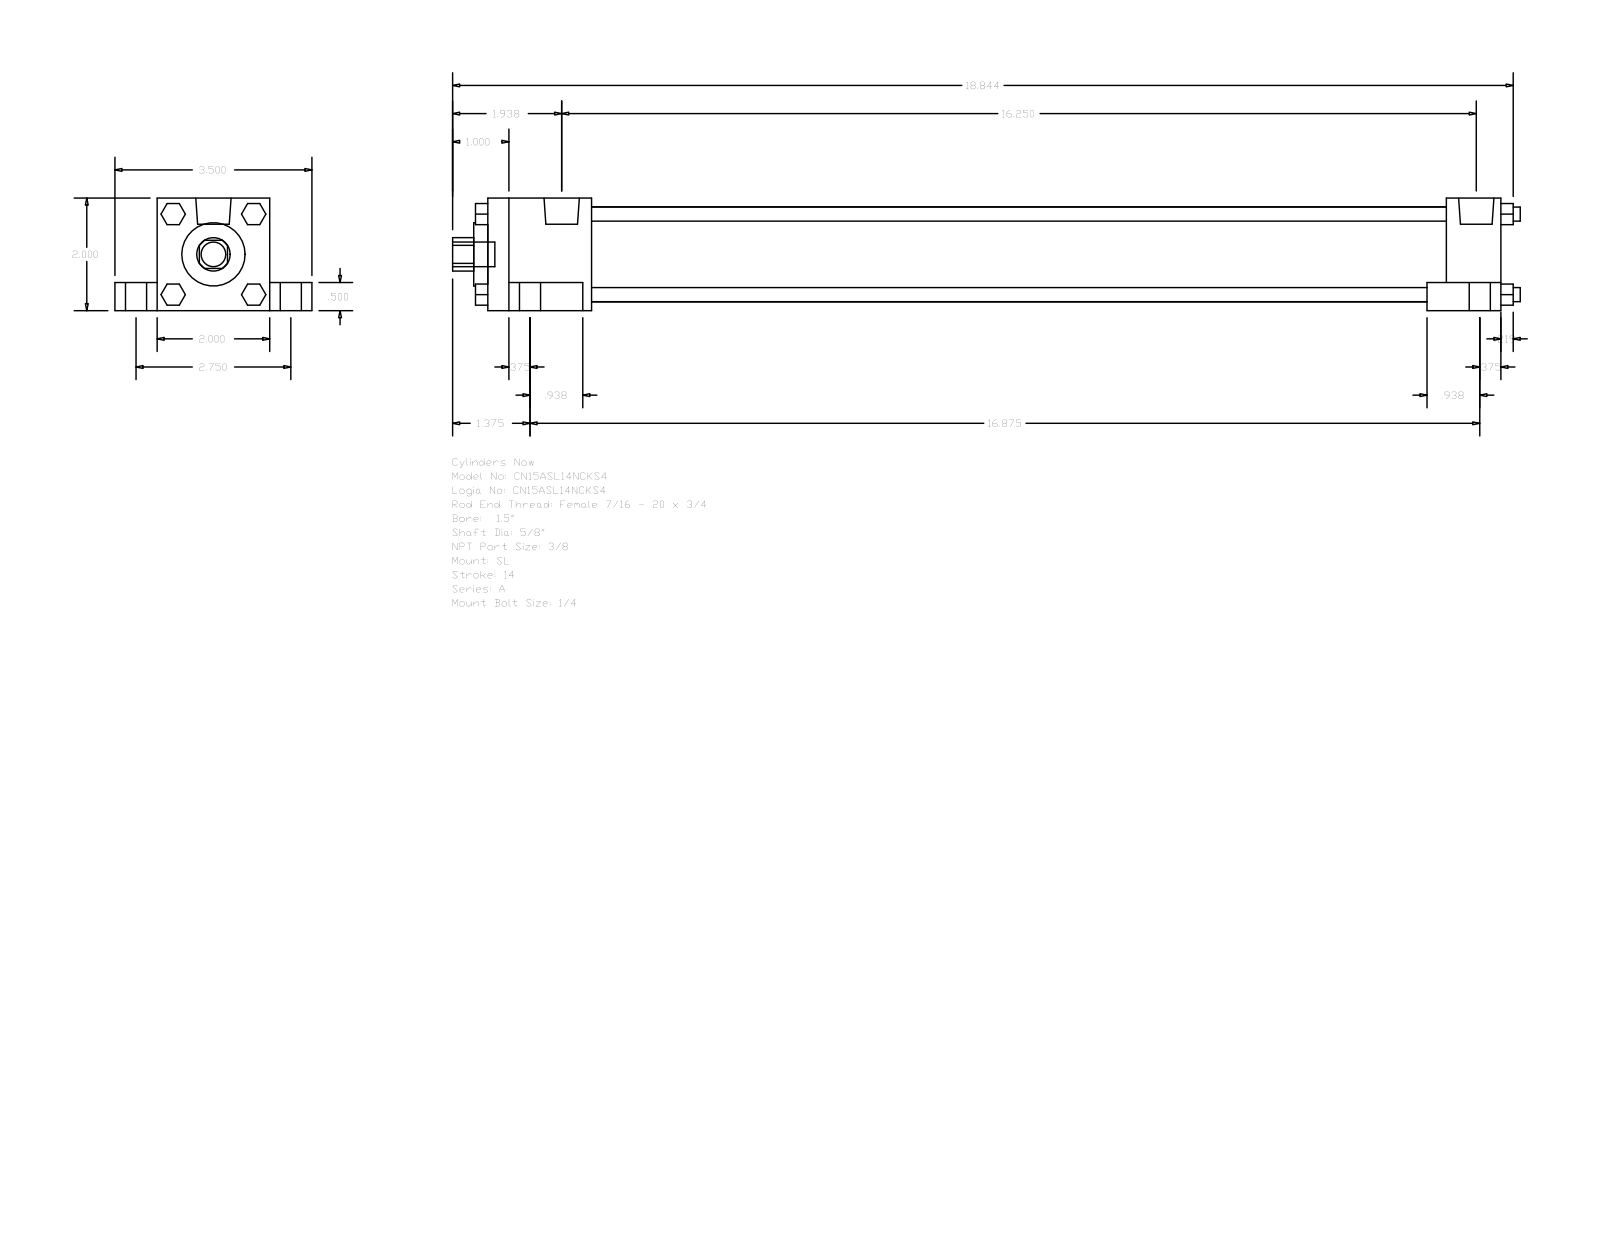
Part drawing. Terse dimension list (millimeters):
name: A_SL__0150_0.625
written by: GSSL Pune (CONFIG_CONTROL_DESIGN)
unit: mm
bodies: 0 solids, 148 faces (112 planar, 36 cylindrical, 0 other)
size: 481.81 × 88.9 × 50.8
holes: 1× ⌀15.88, 1× ⌀28.57, 1× ⌀42.93
bosses: 4× ⌀15.88, 4× ⌀9.53, 4× ⌀6.35, 4× ⌀5.56, 2× ⌀15.93, 1× ⌀11.11
rounds: 1× R7.54
face distances: 50.8, 19.05, 12.7, 38.1, 69.85, 457.19, 9.52, 432.59, 24.6, 46.83
